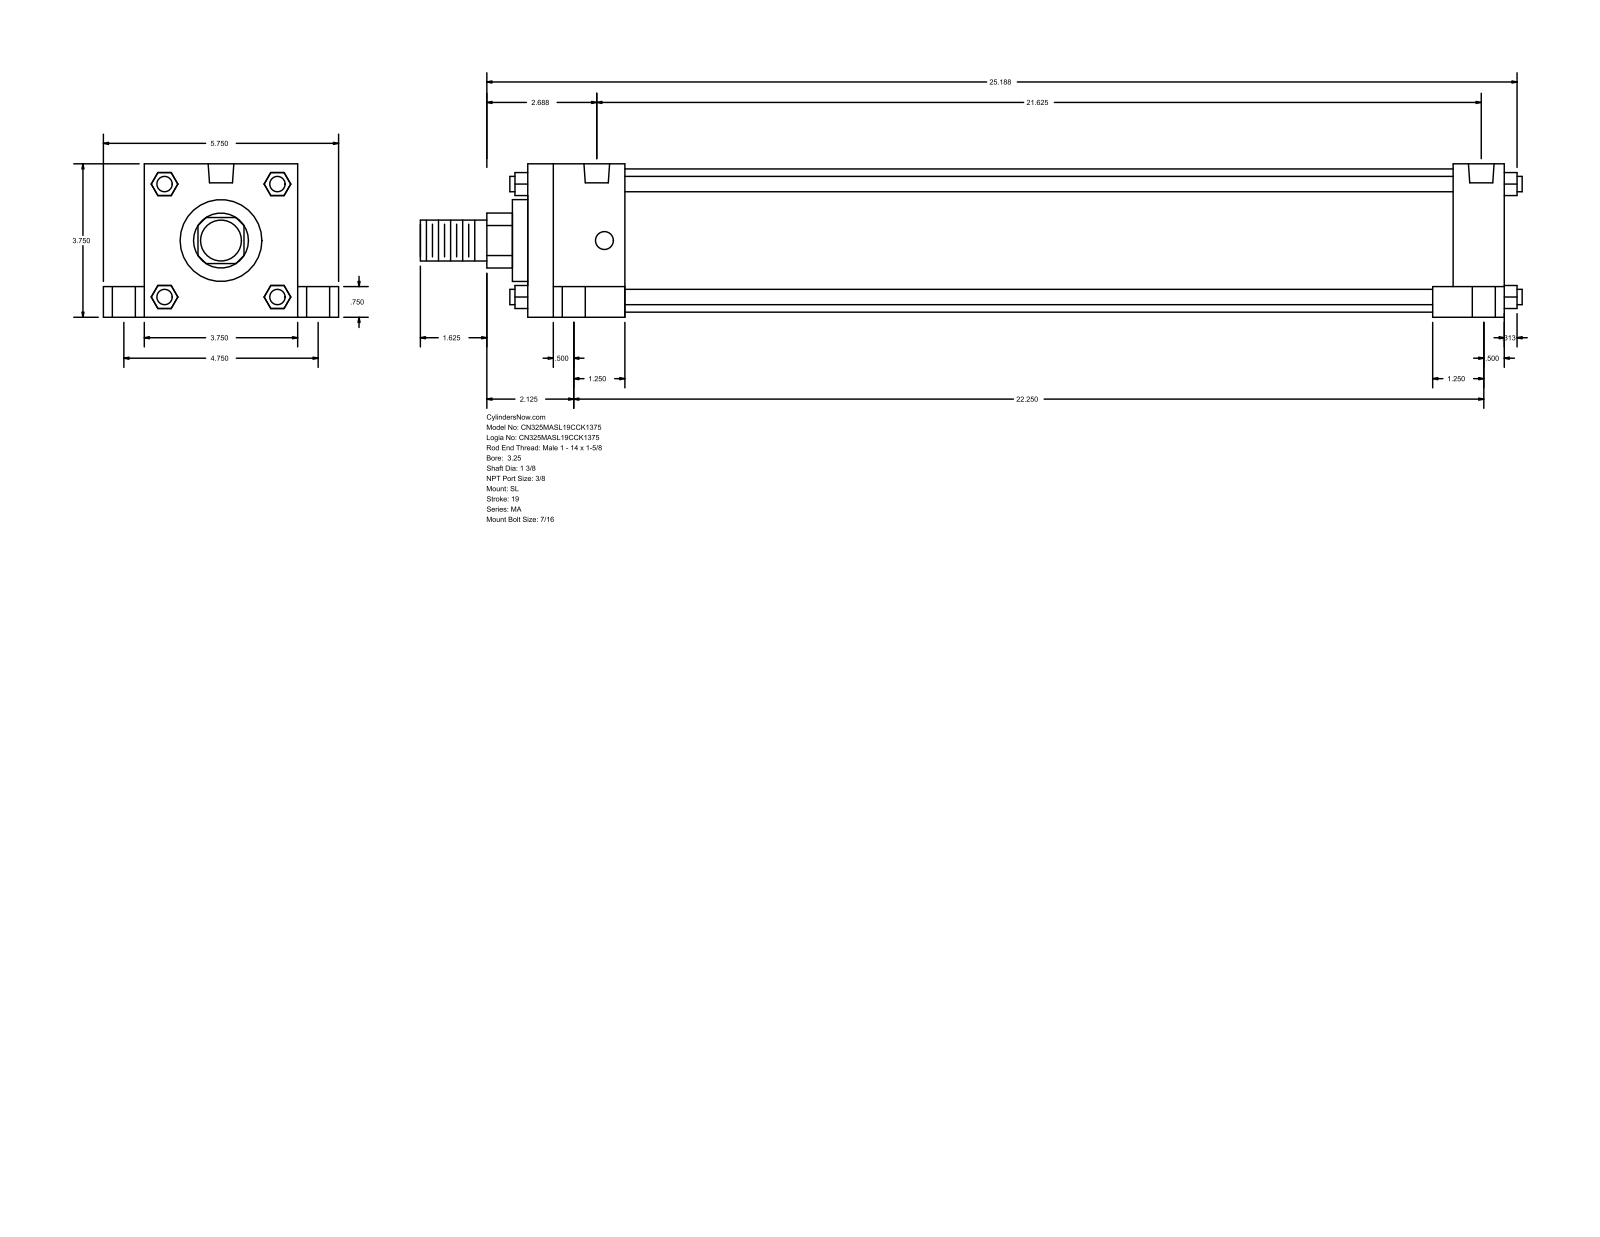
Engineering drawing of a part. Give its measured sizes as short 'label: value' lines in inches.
name: MA_SL__0325_1.375
written by: GSSL Pune (CONFIG_CONTROL_DESIGN)
unit: in
bodies: 0 solids, 148 faces (112 planar, 36 cylindrical, 0 other)
size: 26.937 × 5.75 × 3.75
holes: 4× ⌀0.437, 4× ⌀0.563, 4× ⌀0.813, 2× ⌀0.627
bosses: 4× ⌀0.375, 1× ⌀3.5, 1× ⌀2, 1× ⌀1.375, 1× ⌀1
rounds: 1× R0.672
face distances: 3.75, 23.875, 1, 4.75, 22.625, 1.25, 2.375, 20.25, 21.5, 0.75
hole spacings: 0.188, 2.376, 2.388, 2.441, 2.491, 4.75, 21.25, 21.437
